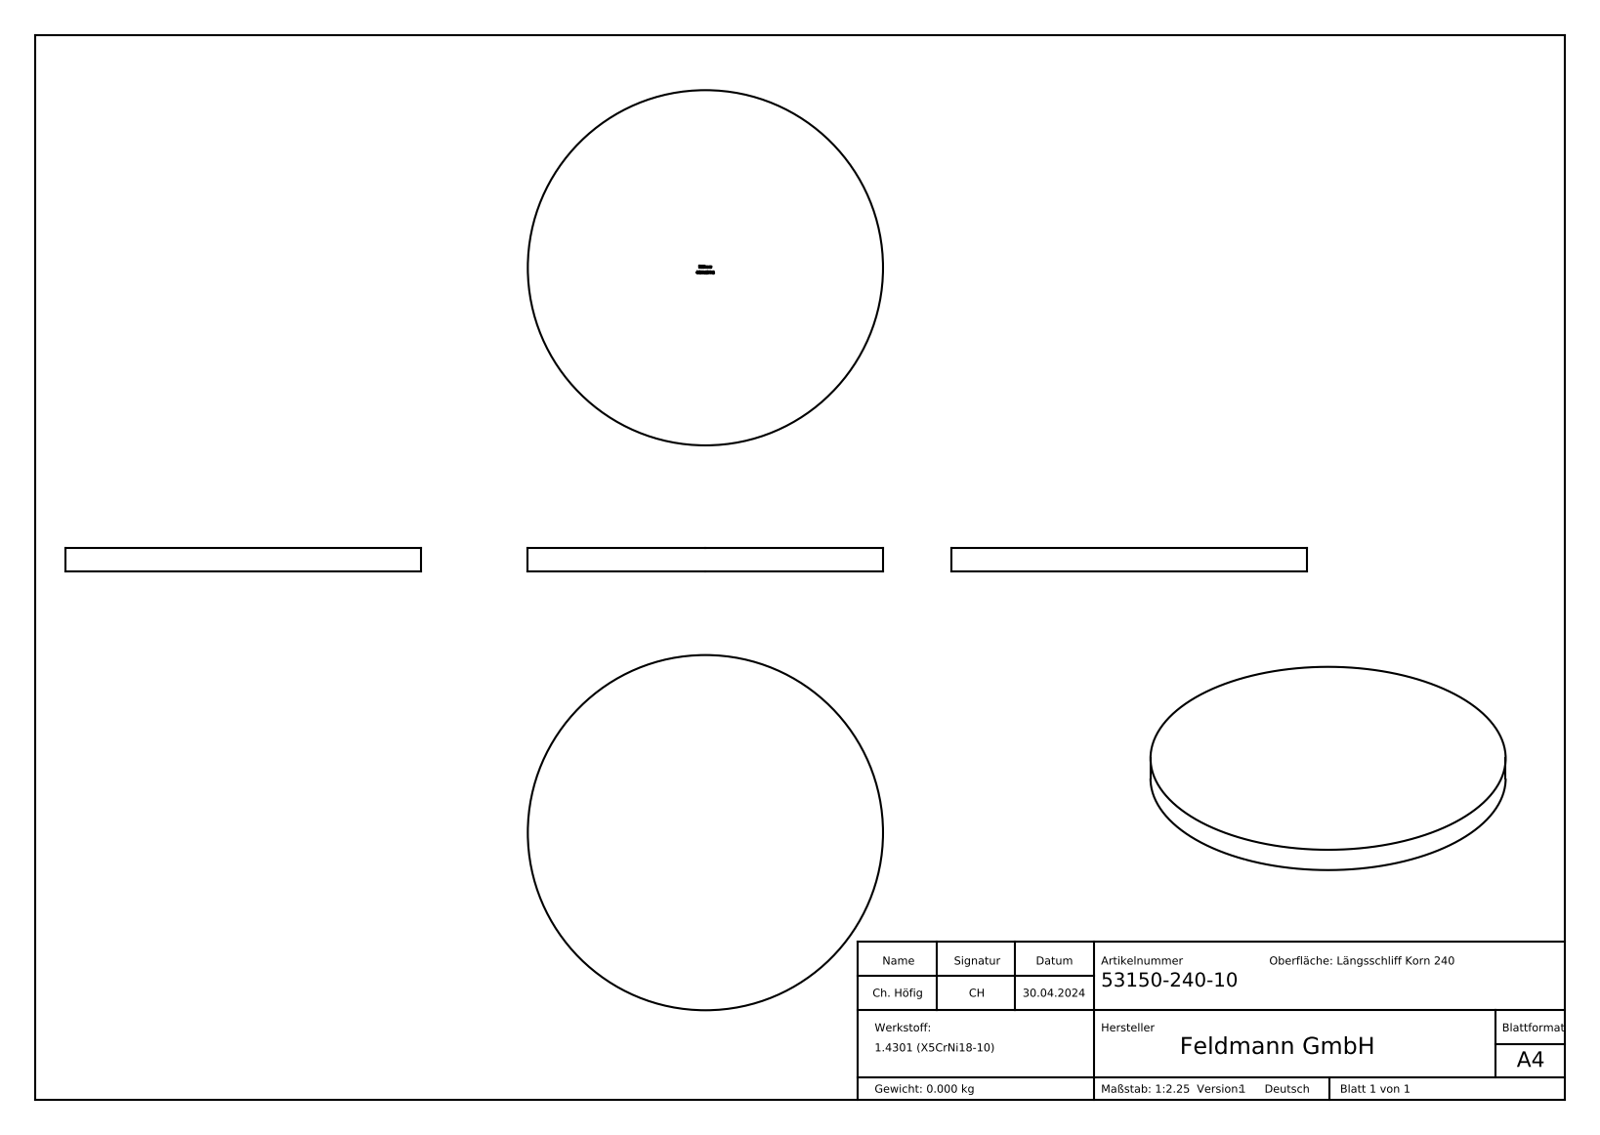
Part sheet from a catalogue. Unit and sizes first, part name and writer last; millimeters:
Units: millimetres
Overall size (bounding box): 150 × 150 × 10
Round bosses / shafts (diameter × count): ⌀150 ×1
Main face-to-face distances: 10, 9.9, 1.06, 2.45, 0.99, 0.39, 2.77, 1.55, 1.78, 0.83
Volume: 176 714 mm³ · Surface area: 40 062 mm²
Bodies: 1 solid, 249 faces (137 planar, 1 cylindrical, 111 other)
Part name (STEP PRODUCT): 53150-240-10
STEP written by: SolidWorks 2018 (CONFIG_CONTROL_DESIGN)
